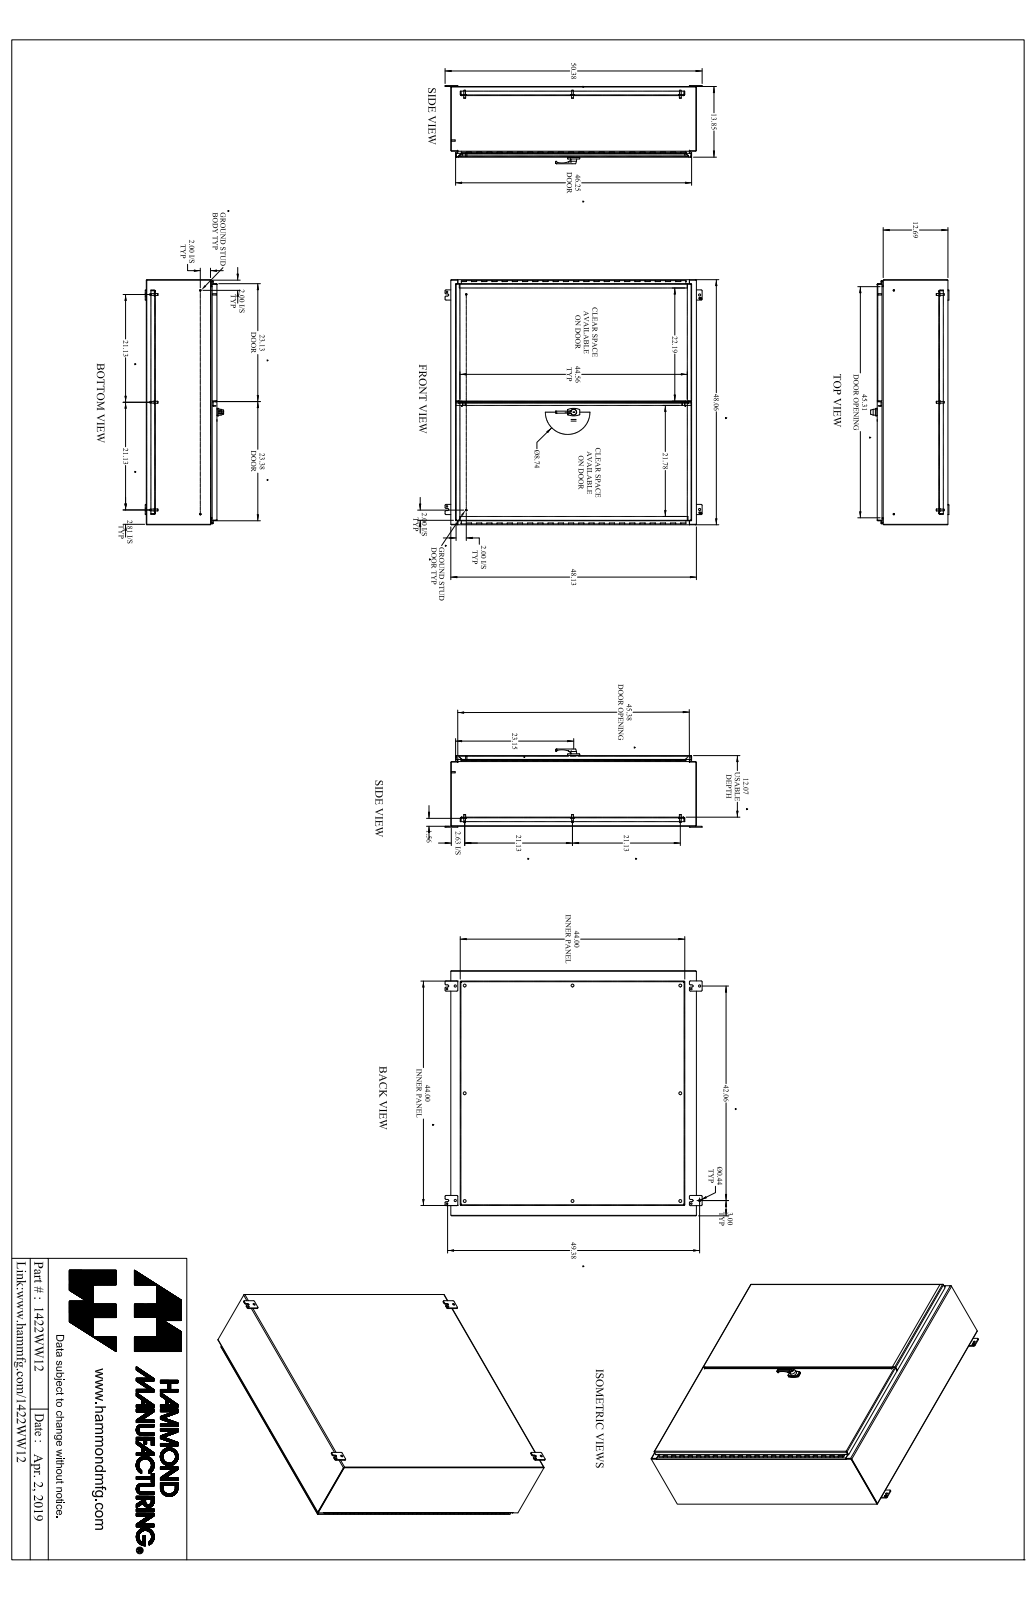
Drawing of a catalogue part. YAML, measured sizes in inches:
part_name: "1422WW12"
step_written_by: "SolidWorks 2019 (AUTOMOTIVE_DESIGN)"
units: inches
bodies: {solids: 0, faces: 1897, planar: 1198, cylindrical: 573, other: 126}
overall_size: [50.375, 48.063, 15.274]
round_holes:
  - {diameter: 0.304, count: 16}
  - {diameter: 0.307, count: 9}
  - {diameter: 0.563, count: 8}
  - {diameter: 0.445, count: 6}
  - {diameter: 0.218, count: 4}
  - {diameter: 0.313, count: 4}
  - {diameter: 0.437, count: 4}
  - {diameter: 0.215, count: 3}
  - {diameter: 0.11, count: 2}
  - {diameter: 0.127, count: 2}
  - {diameter: 0.156, count: 2}
  - {diameter: 0.187, count: 2}
round_bosses_or_shafts:
  - {diameter: 1, count: 9}
  - {diameter: 0.65, count: 8}
  - {diameter: 0.375, count: 8}
  - {diameter: 0.33, count: 8}
  - {diameter: 0.5, count: 5}
  - {diameter: 0.313, count: 4}
  - {diameter: 0.281, count: 4}
  - {diameter: 0.25, count: 4}
partial_cylinders:
  - {radius: 0.048, count: 32}
  - {radius: 0.143, count: 32}
  - {radius: 0.188, count: 27}
  - {radius: 0.05, count: 16}
  - {radius: 0.116, count: 12}
  - {radius: 0.187, count: 12}
  - {radius: 0.062, count: 8}
  - {radius: 0.218, count: 8}
face_to_face_distances: [0.095, 13.752, 13.657, 13.847, 0.125, 12.191, 12.096, 12.065, 11.97, 1.687]
hole_center_spacings: [6, 46.778, 12, 47.919, 18, 49.762, 24, 46.392]
